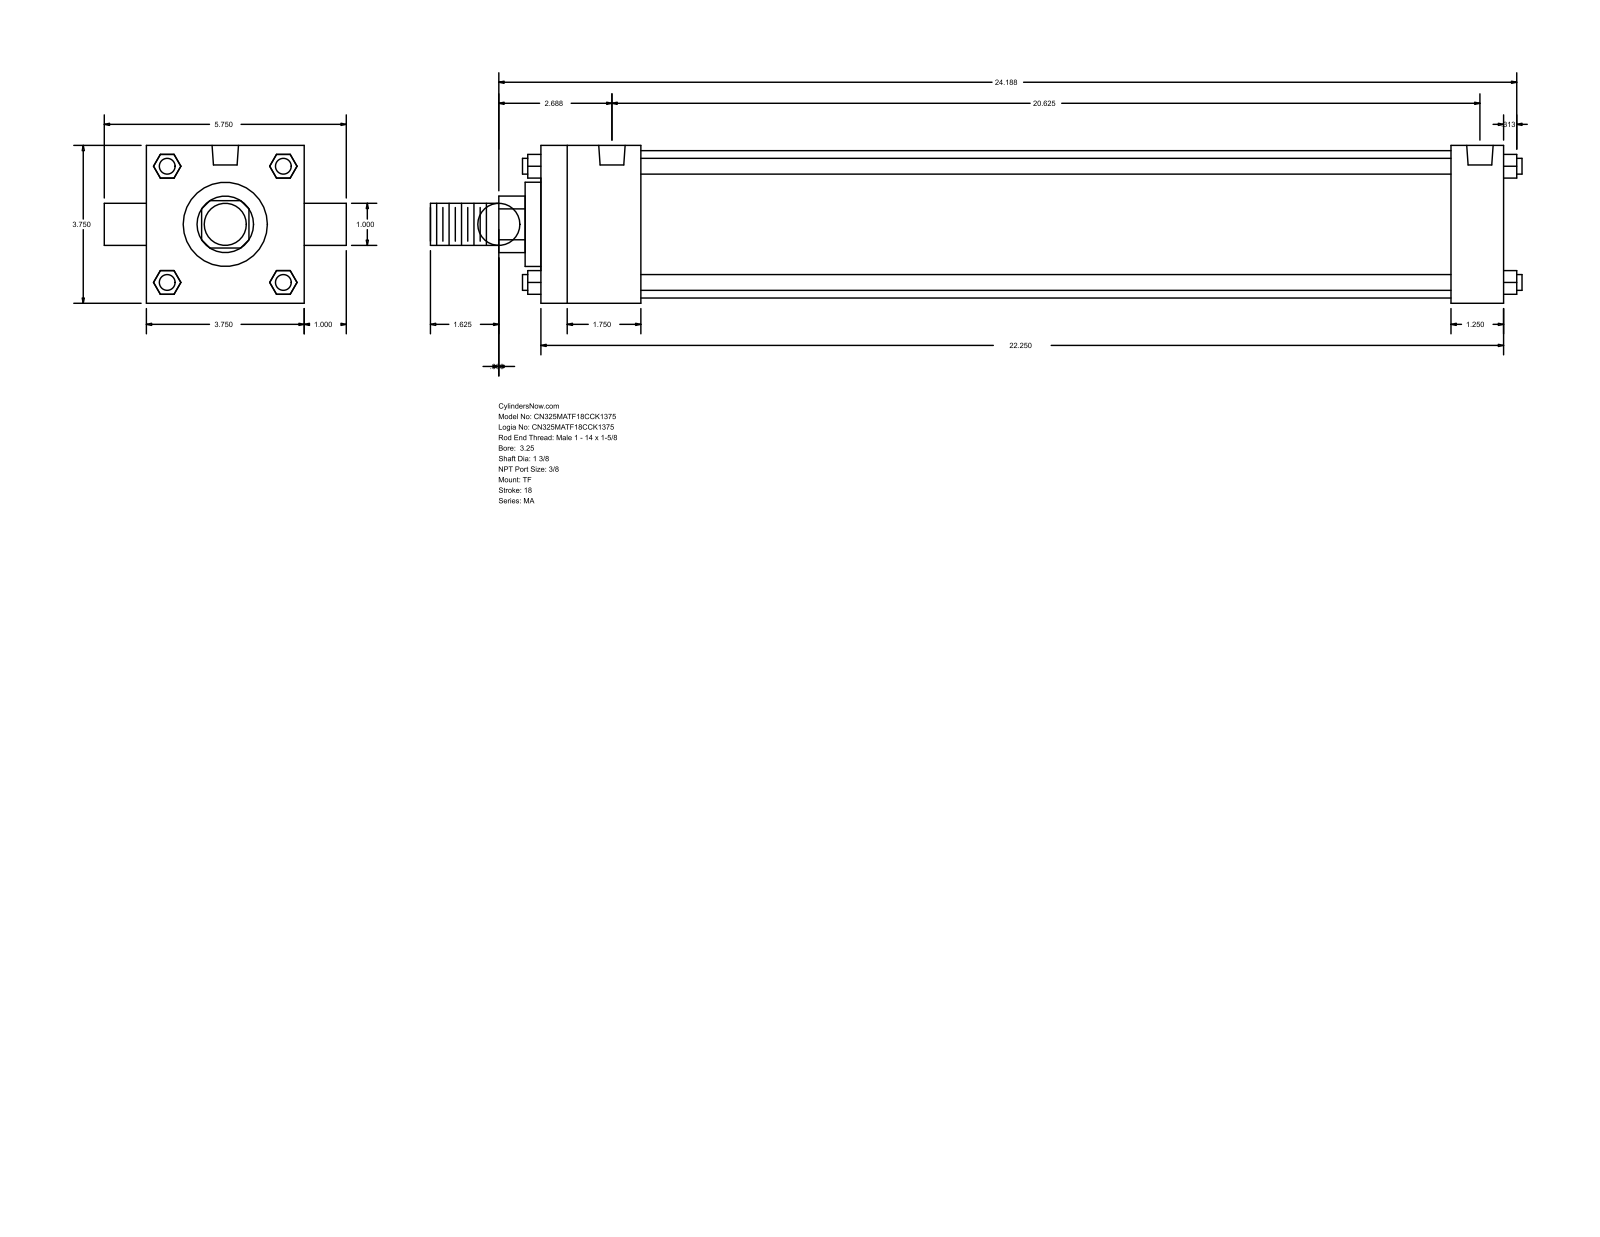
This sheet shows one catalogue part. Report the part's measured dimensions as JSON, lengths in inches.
{"part_name": "MA_TF__0325_1.375", "step_written_by": "GSSL Pune (CONFIG_CONTROL_DESIGN)", "units": "inches", "bodies": {"solids": 0, "faces": 120, "planar": 92, "cylindrical": 28, "other": 0}, "overall_size": [25.937, 5.75, 3.75], "round_holes": [[0.437, 3], [0.627, 2]], "round_bosses_or_shafts": [[0.375, 4], [1, 2], [3.5, 1], [2, 1], [1.375, 1]], "partial_cylinders_radius": [[0.672, 1]], "face_to_face_distances": [3.75, 22.875, 2.375, 21.625, 19.25, 20.5, 1.25, 0.375, 2.75, 22], "hole_center_spacings": [0.187, 0.188, 20.25, 20.437, 20.438, 20.625]}
